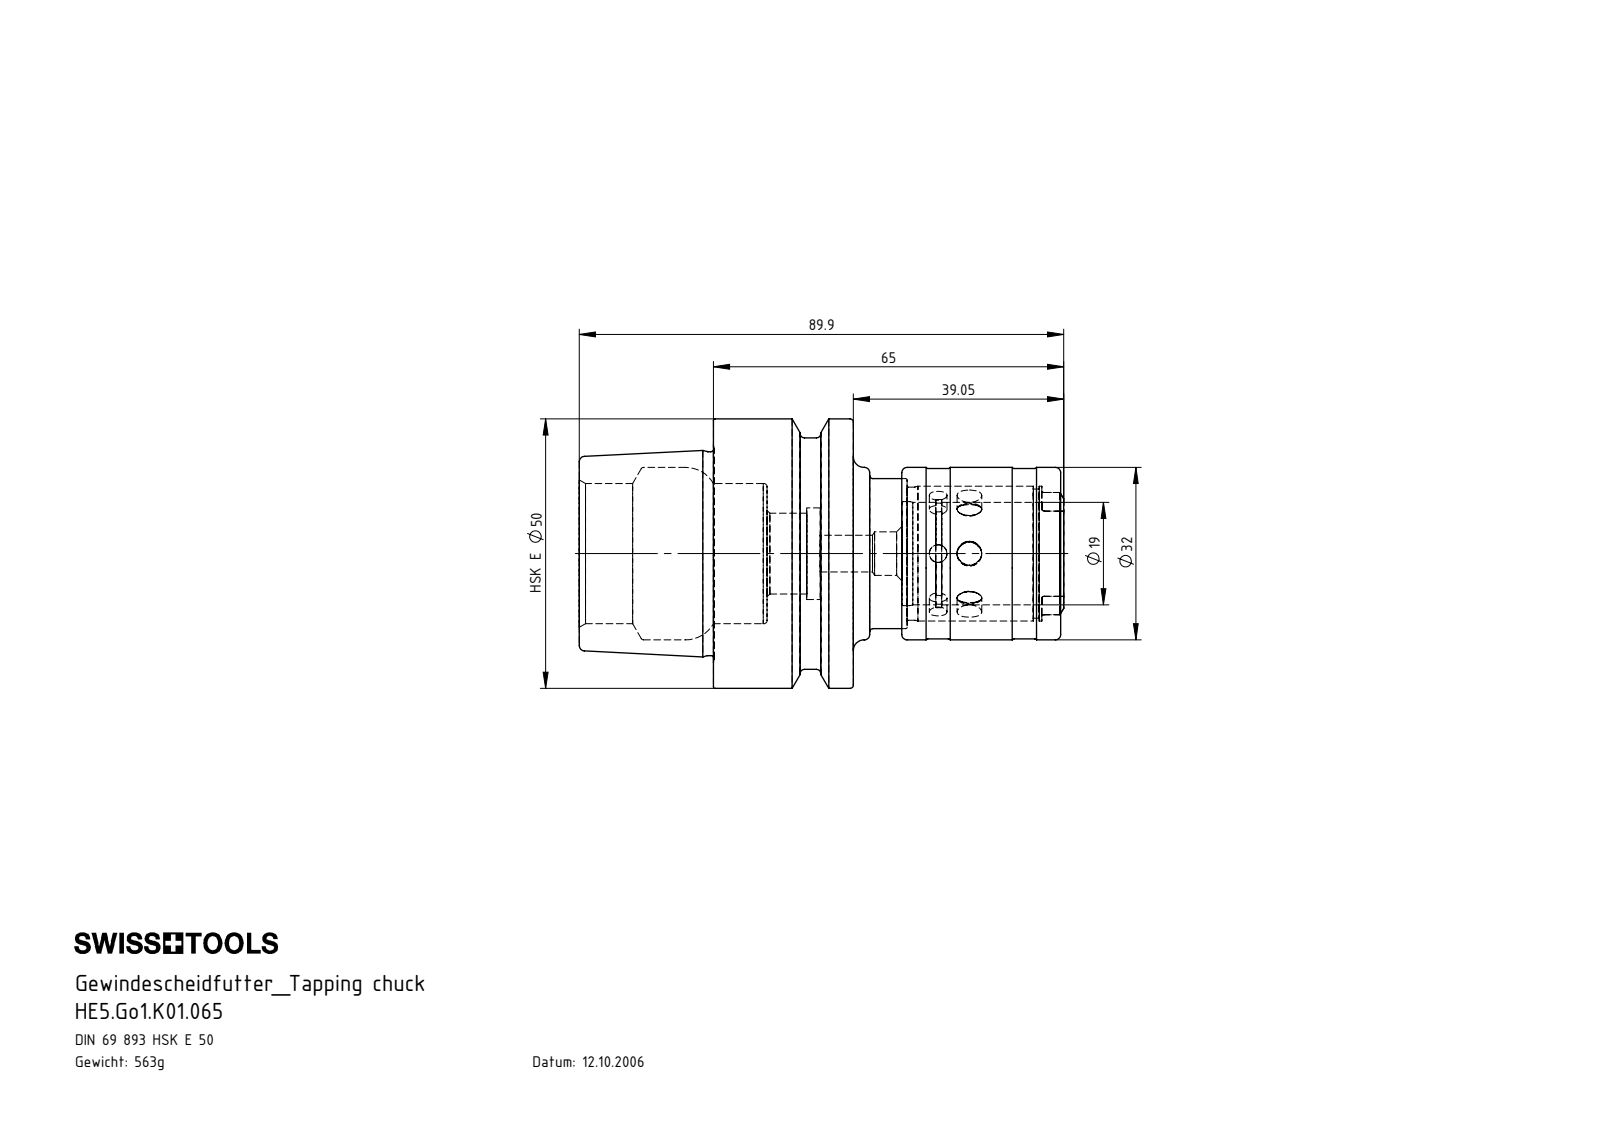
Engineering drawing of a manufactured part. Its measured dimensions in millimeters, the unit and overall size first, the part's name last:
Units: millimetres
Overall size (bounding box): 89.9 × 50 × 50
Round holes (diameter × count): ⌀3.3 ×3, ⌀4.6 ×3, ⌀2 ×1, ⌀6.8 ×1, ⌀8 ×1, ⌀8.1 ×1, ⌀15 ×1, ⌀17 ×1, ⌀19 ×1, ⌀19.3 ×1, ⌀20.05 ×1, ⌀25 ×1
Round bosses / shafts (diameter × count): ⌀50 ×1, ⌀42.95 ×1, ⌀37.81 ×1, ⌀32 ×1, ⌀31.6 ×1, ⌀27.85 ×1, ⌀24.7 ×1, ⌀23.95 ×1
Partial cylindrical surfaces — rounded edges, fillets, slot ends (radius × count): R2.15 ×3, R0.5 ×2
Main face-to-face distances: 25.95, 9.95, 24.9, 50.85, 34.85, 16, 68.8, 43.9, 33.95, 17.95
Hole centre spacings: 5.8
Volume: 71 762 mm³ · Surface area: 29 697 mm²
Bodies: 10 solids, 303 faces (51 planar, 97 cylindrical, 155 other)
Part name (STEP PRODUCT): HE5-Go1.K01.065_A_Fertigbearbeitung; Go1-ER1.019.008_A; Go1-ER4.001.005; Go1-ER2.028.032_vorgespannt (+6 more)
STEP written by: SolidWorks 2017 (AUTOMOTIVE_DESIGN)
